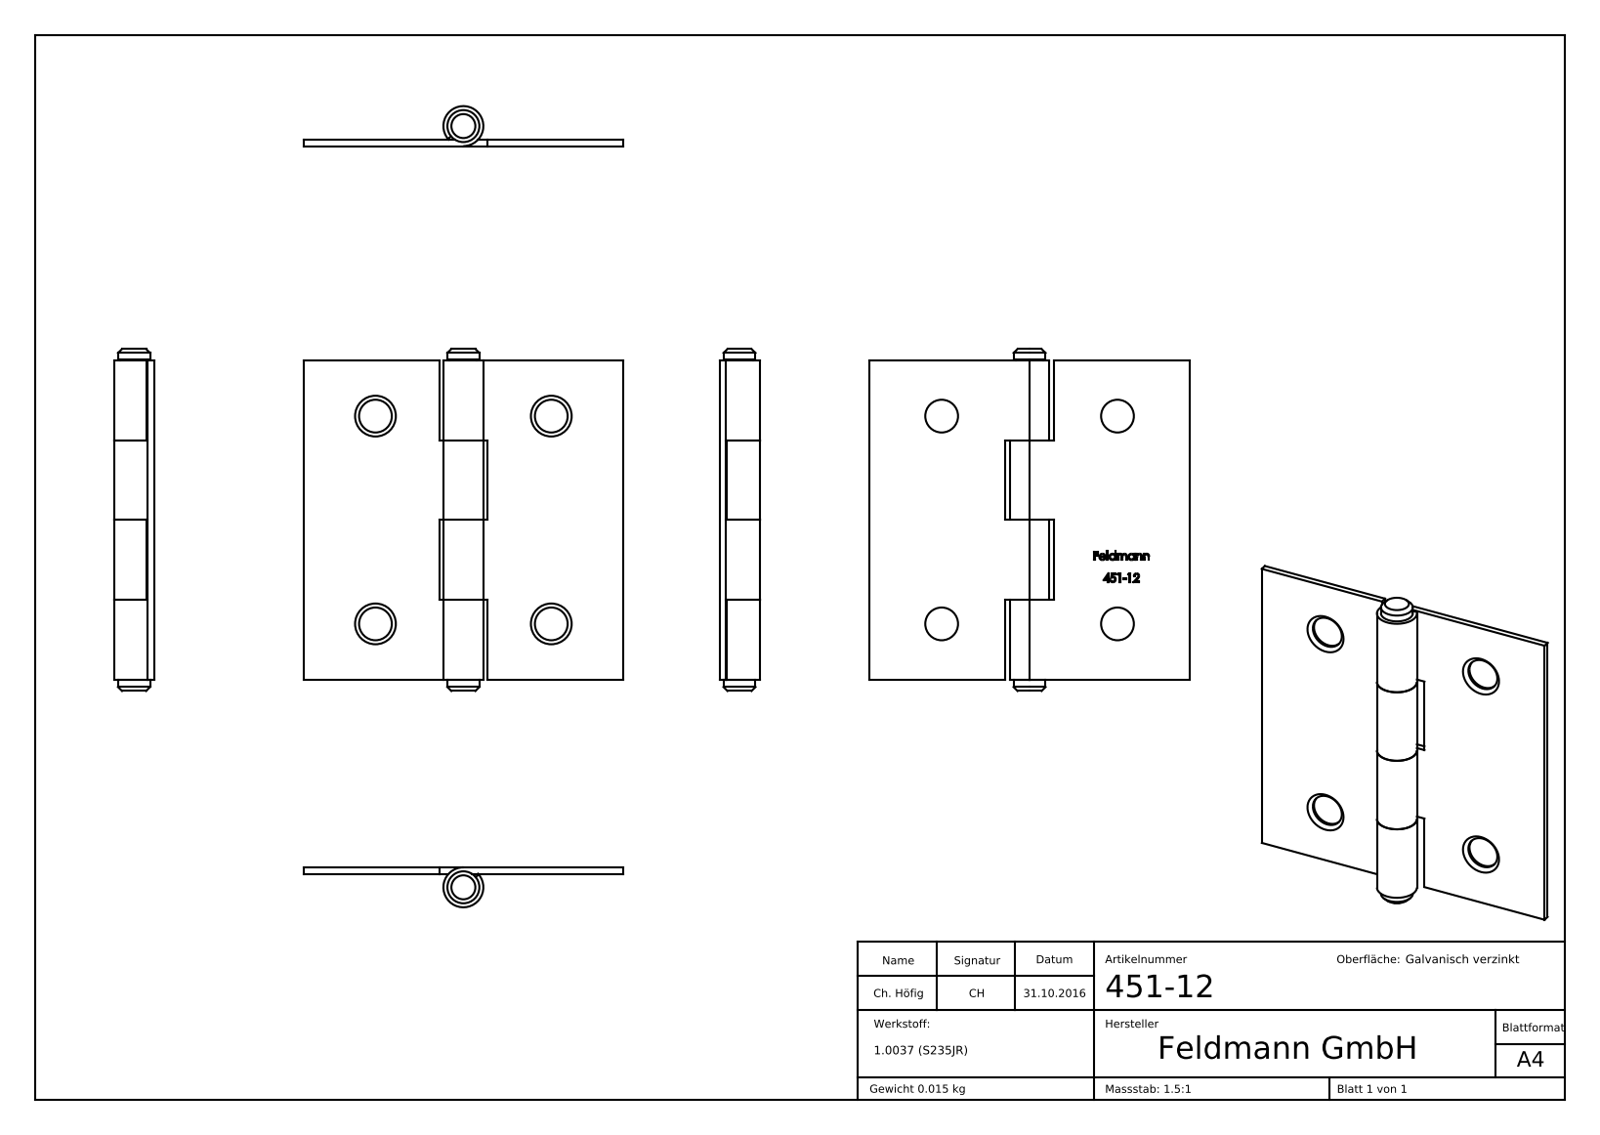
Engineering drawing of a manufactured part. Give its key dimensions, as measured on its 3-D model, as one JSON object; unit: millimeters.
{"part_name": "451-12 Teil1; 451-12 Teil3; 451-12; 451-12 Teil2", "step_written_by": "SolidWorks 2018 (CONFIG_CONTROL_DESIGN)", "units": "millimeters", "bodies": {"solids": 3, "faces": 224, "planar": 141, "cylindrical": 15, "other": 68}, "overall_size": [42.8, 40, 5], "volume_mm3": 1893, "surface_area_mm2": 4551, "round_holes": [[4.1, 4], [3.4, 1]], "round_bosses_or_shafts": [[5, 1], [4, 1]], "face_to_face_distances": [0.8, 10, 40, 20, 30, 17, 23, 6, 1.4, 11.4], "hole_center_spacings": [22, 26, 34.06]}
